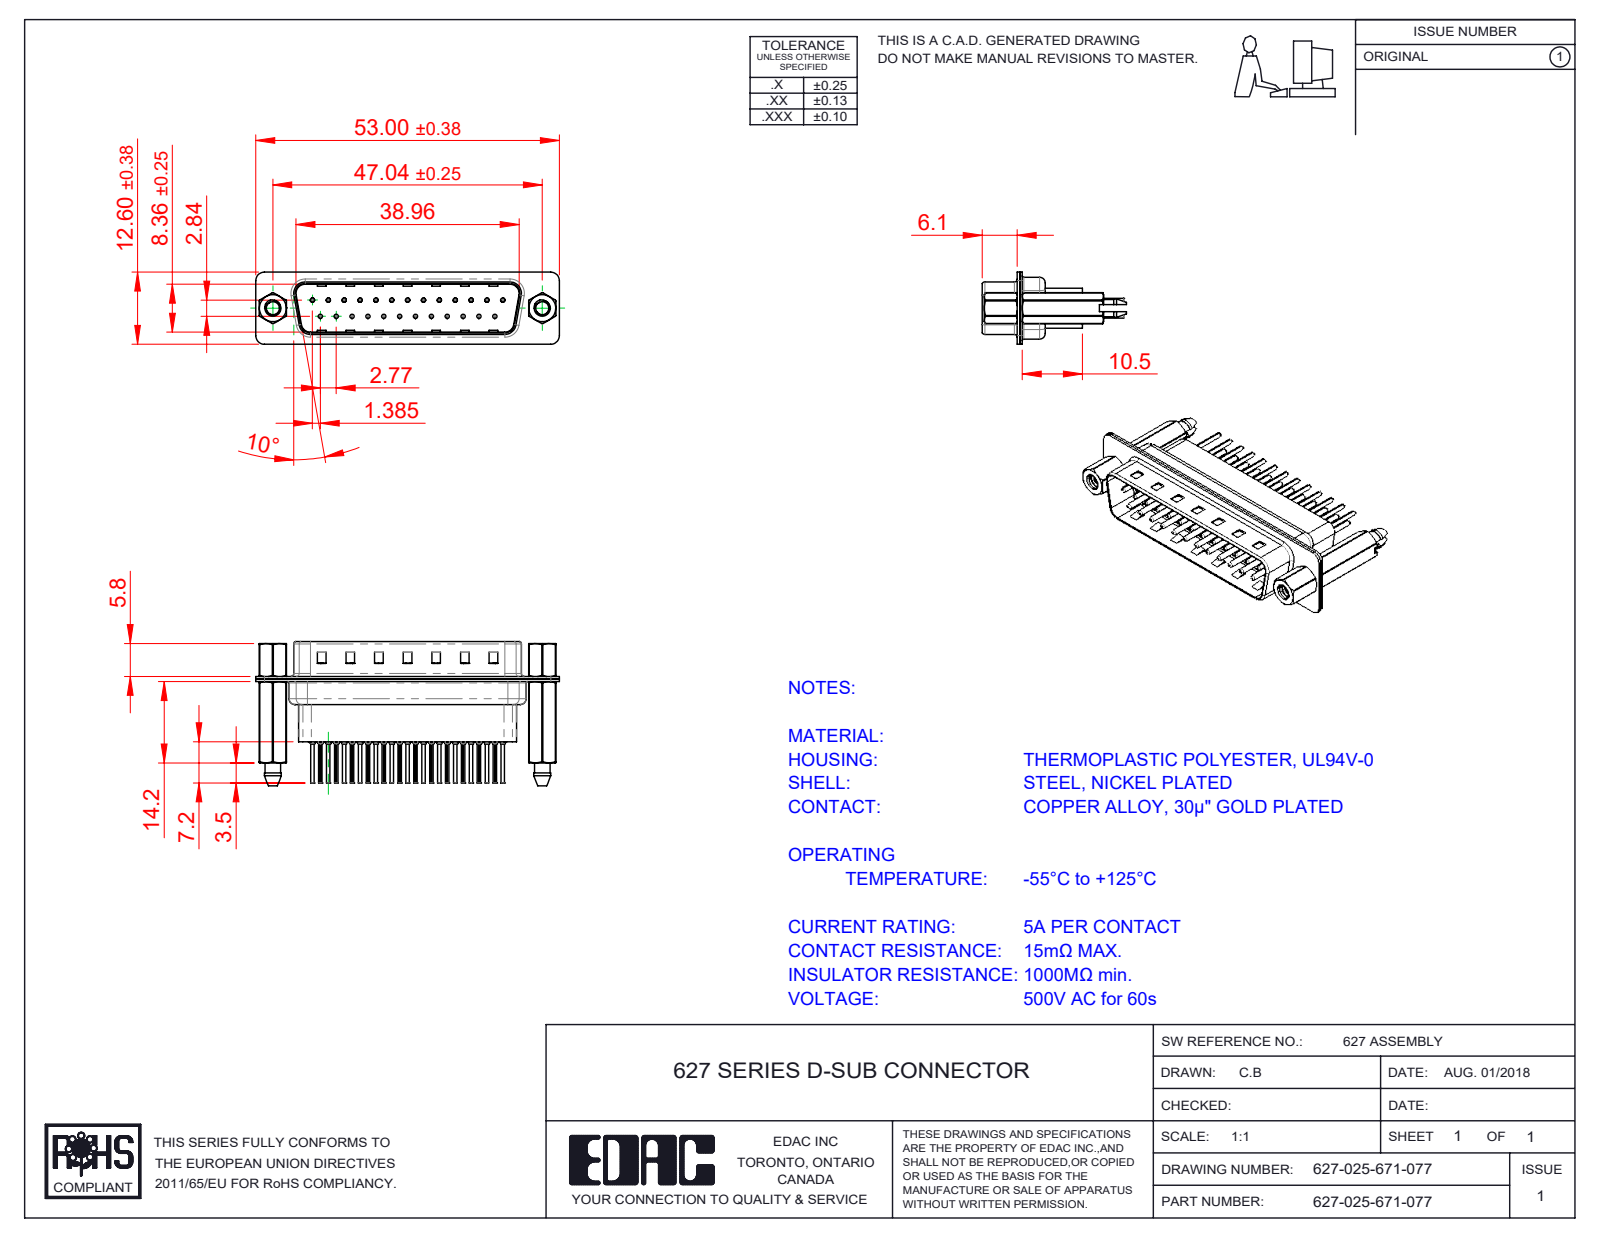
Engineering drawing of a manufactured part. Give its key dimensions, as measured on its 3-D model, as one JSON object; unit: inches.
{"part_name": "627 Contact Row 1_61; 627 Contact Row 2_61; 627 4-40 Hex Standoff; 627 Shell Front_25 Contacts (+4 more)", "step_written_by": "SolidWorks 2020 (CONFIG_CONTROL_DESIGN)", "units": "inches", "bodies": {"solids": 32, "faces": 3060, "planar": 825, "cylindrical": 1200, "other": 1035}, "overall_size": [2.087, 0.988, 0.496], "volume_in3": 0.268, "surface_area_in2": 17.48, "round_holes": [[0.008, 25], [0.014, 25], [0.043, 25], [0.063, 25], [0.089, 2], [0.09, 2], [0.157, 2], [0.189, 2]], "round_bosses_or_shafts": [[0.079, 25], [0.059, 25], [0.03, 25], [0.024, 25], [0.193, 2], [0.11, 2]], "partial_cylinders_radius": [[0.004, 50], [0.059, 18], [0.079, 12], [0.063, 10], [0.02, 8], [0.01, 4], [0.024, 4], [0.026, 4]], "face_to_face_distances": [0.016, 0.018, 0.032, 0.377, 0.027, 0.302, 0.059, 0.035, 0.043, 0.318], "hole_center_spacings": [0.124, 0.327, 0.109, 0.218, 0.436, 0.654, 0.198, 0.198]}
